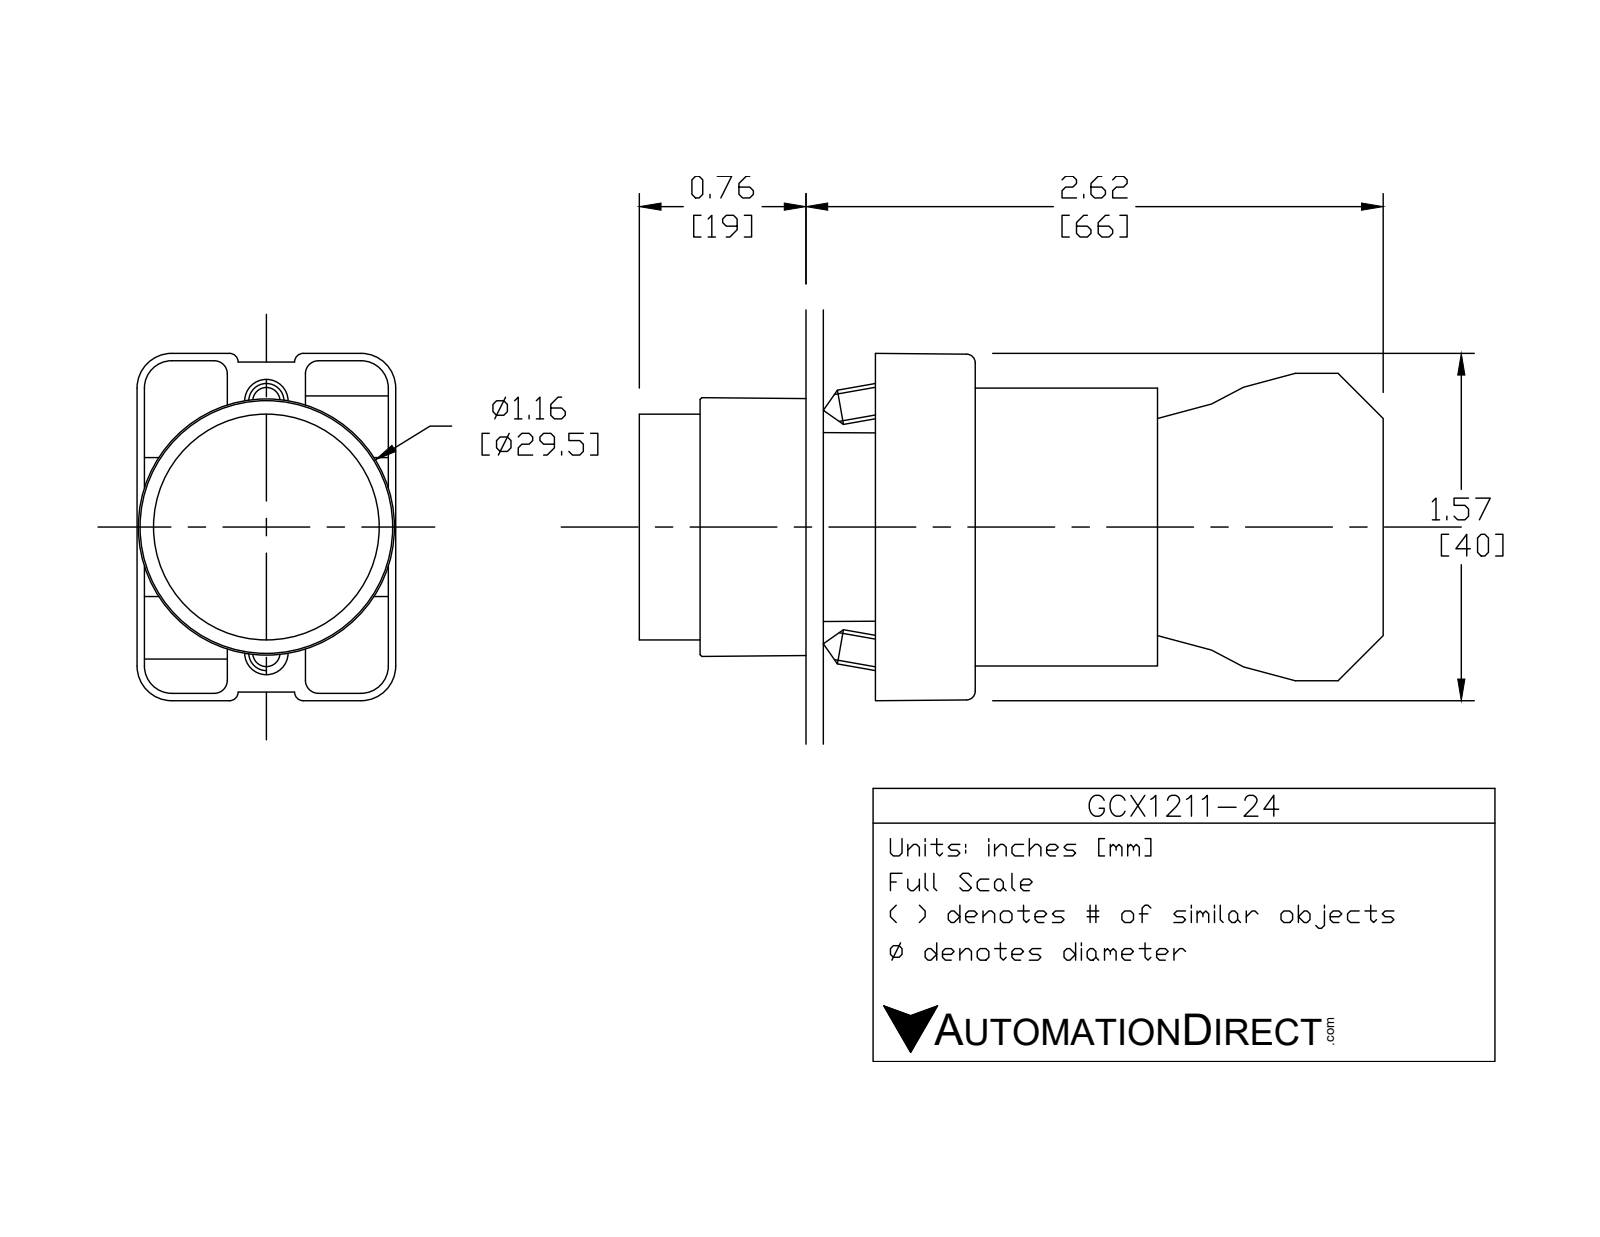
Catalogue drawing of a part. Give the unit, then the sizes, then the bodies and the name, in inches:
Units: inches
Overall size (bounding box): 3.319 × 1.581 × 1.177
Round holes (diameter × count): ⌀0.079 ×2, ⌀0.124 ×2, ⌀0.13 ×2, ⌀0.087 ×1, ⌀0.197 ×1, ⌀0.469 ×1, ⌀0.878 ×1, ⌀0.888 ×1, ⌀1.024 ×1
Round bosses / shafts (diameter × count): ⌀0.157 ×4, ⌀1.175 ×1, ⌀1.004 ×1, ⌀0.945 ×1, ⌀0.856 ×1, ⌀0.78 ×1, ⌀0.504 ×1
Partial cylindrical surfaces — rounded edges, fillets, slot ends (radius × count): R0.059 ×24, R0.041 ×12, R0.124 ×12, R0.157 ×12, R0.039 ×8, R0.128 ×2, R0.02 ×1, R0.063 ×1
Main face-to-face distances: 0.827, 0.579, 1.171, 2.02, 1.193, 0.031, 0.033, 0.573, 1.165, 0.593
Hole centre spacings: 0.236, 0.544, 0.472, 0.49
Volume: 2.721 in³ · Surface area: 36.32 in²
Bodies: 7 solids, 425 faces (250 planar, 144 cylindrical, 31 other)
Part name (STEP PRODUCT): GCX1211-24; ecx1030; ecx1029; GCX1211 OPERATOR (+1 more)
STEP written by: SolidWorks 2016 (AUTOMOTIVE_DESIGN)
